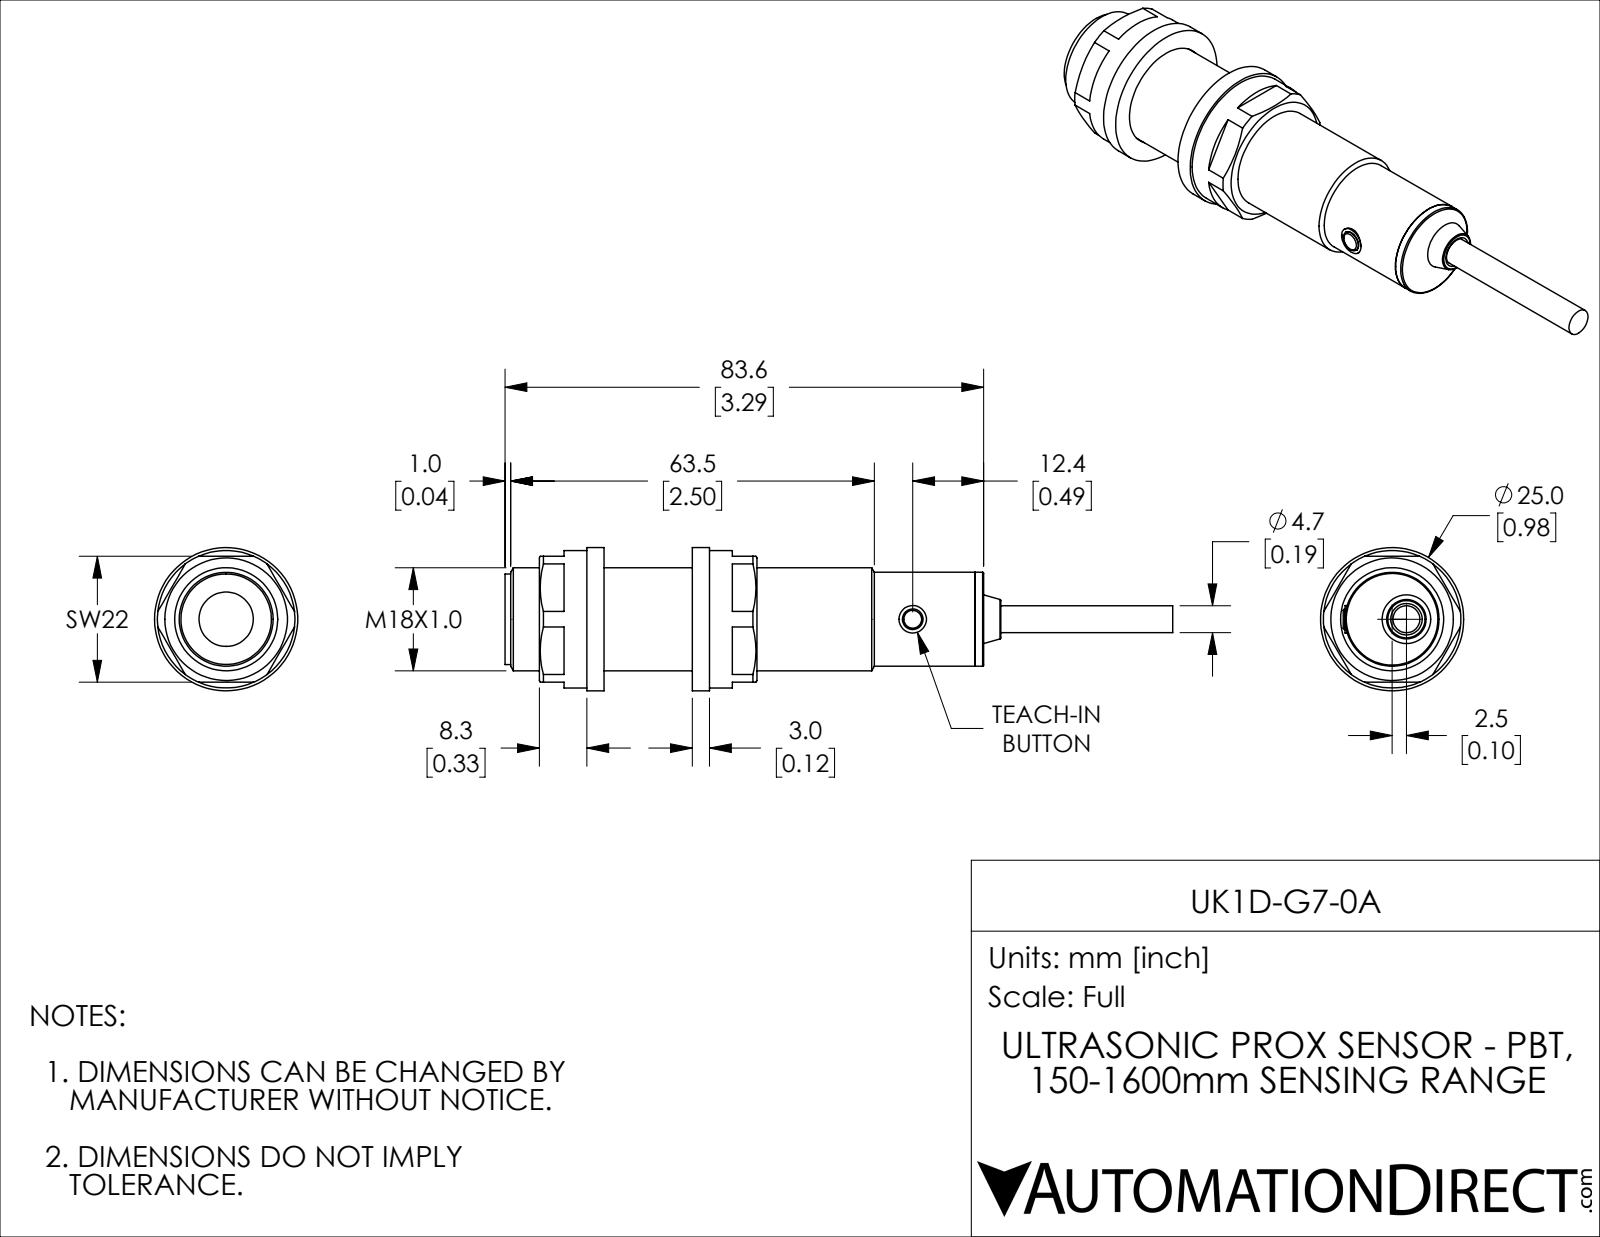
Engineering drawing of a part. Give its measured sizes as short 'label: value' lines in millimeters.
name: UK1D-G7-0A
written by: SolidWorks 2018 (AUTOMOTIVE_DESIGN)
unit: mm
bodies: 10 solids, 107 faces (49 planar, 40 cylindrical, 18 other)
size: 116.6 × 25 × 25
volume: 25 220 mm³; area: 11 419 mm²
holes: 2× ⌀4.7, 1× ⌀3.6, 1× ⌀9.5, 1× ⌀18, 1× ⌀18.2
bosses: 1× ⌀25, 1× ⌀24, 1× ⌀16.4, 1× ⌀15.8, 1× ⌀5.4, 1× ⌀4.8
face distances: 3, 18.4, 21.4, 67.8, 46.4, 13.3, 34.7, 81.1, 16.3, 64.8
hole spacings: 2.5
